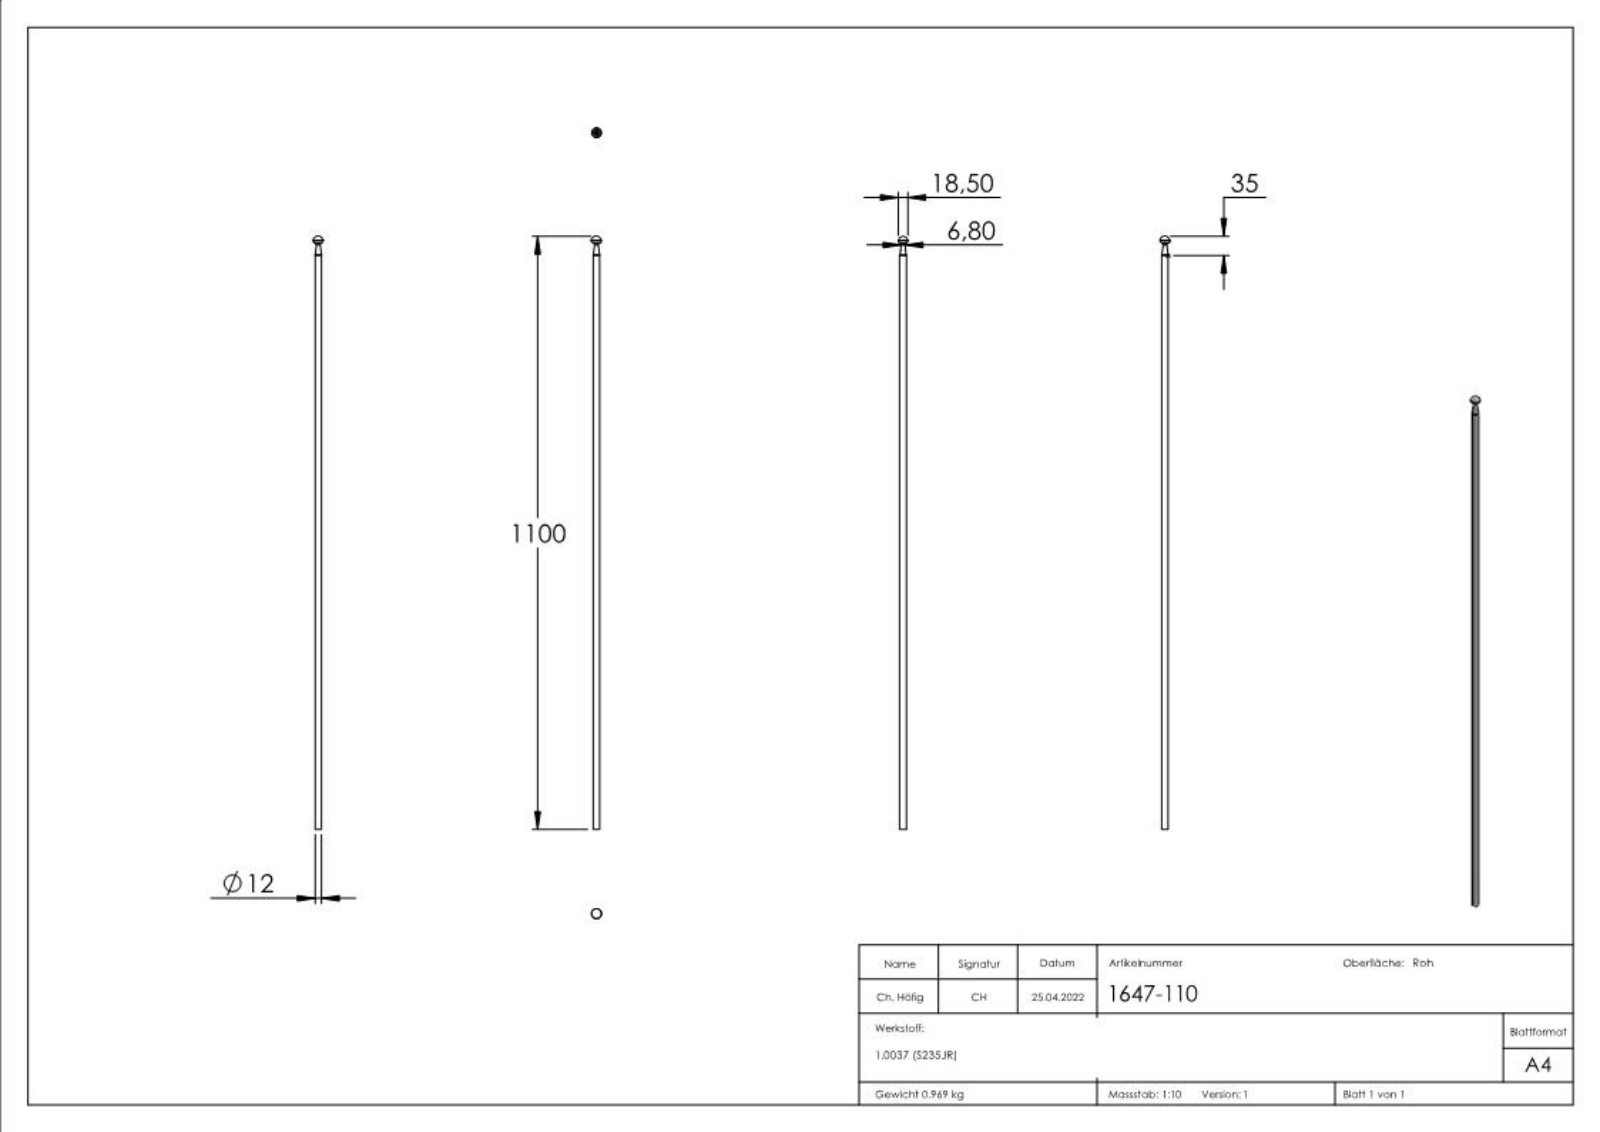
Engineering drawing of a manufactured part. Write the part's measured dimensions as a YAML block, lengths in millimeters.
part_name: "1647-110"
step_written_by: "SolidWorks 2018 (CONFIG_CONTROL_DESIGN)"
units: millimeters
bodies: {solids: 1, faces: 237, planar: 144, cylindrical: 1, other: 92}
overall_size: [1100, 18.5, 18.5]
volume: 124207
surface_area: 41718
round_bosses_or_shafts:
  - {diameter: 12, count: 1}
face_to_face_distances: [1.87, 0.61, 0.34, 0.32, 2.9, 2.12, 1.99, 0.96, 0.69, 0.53]
